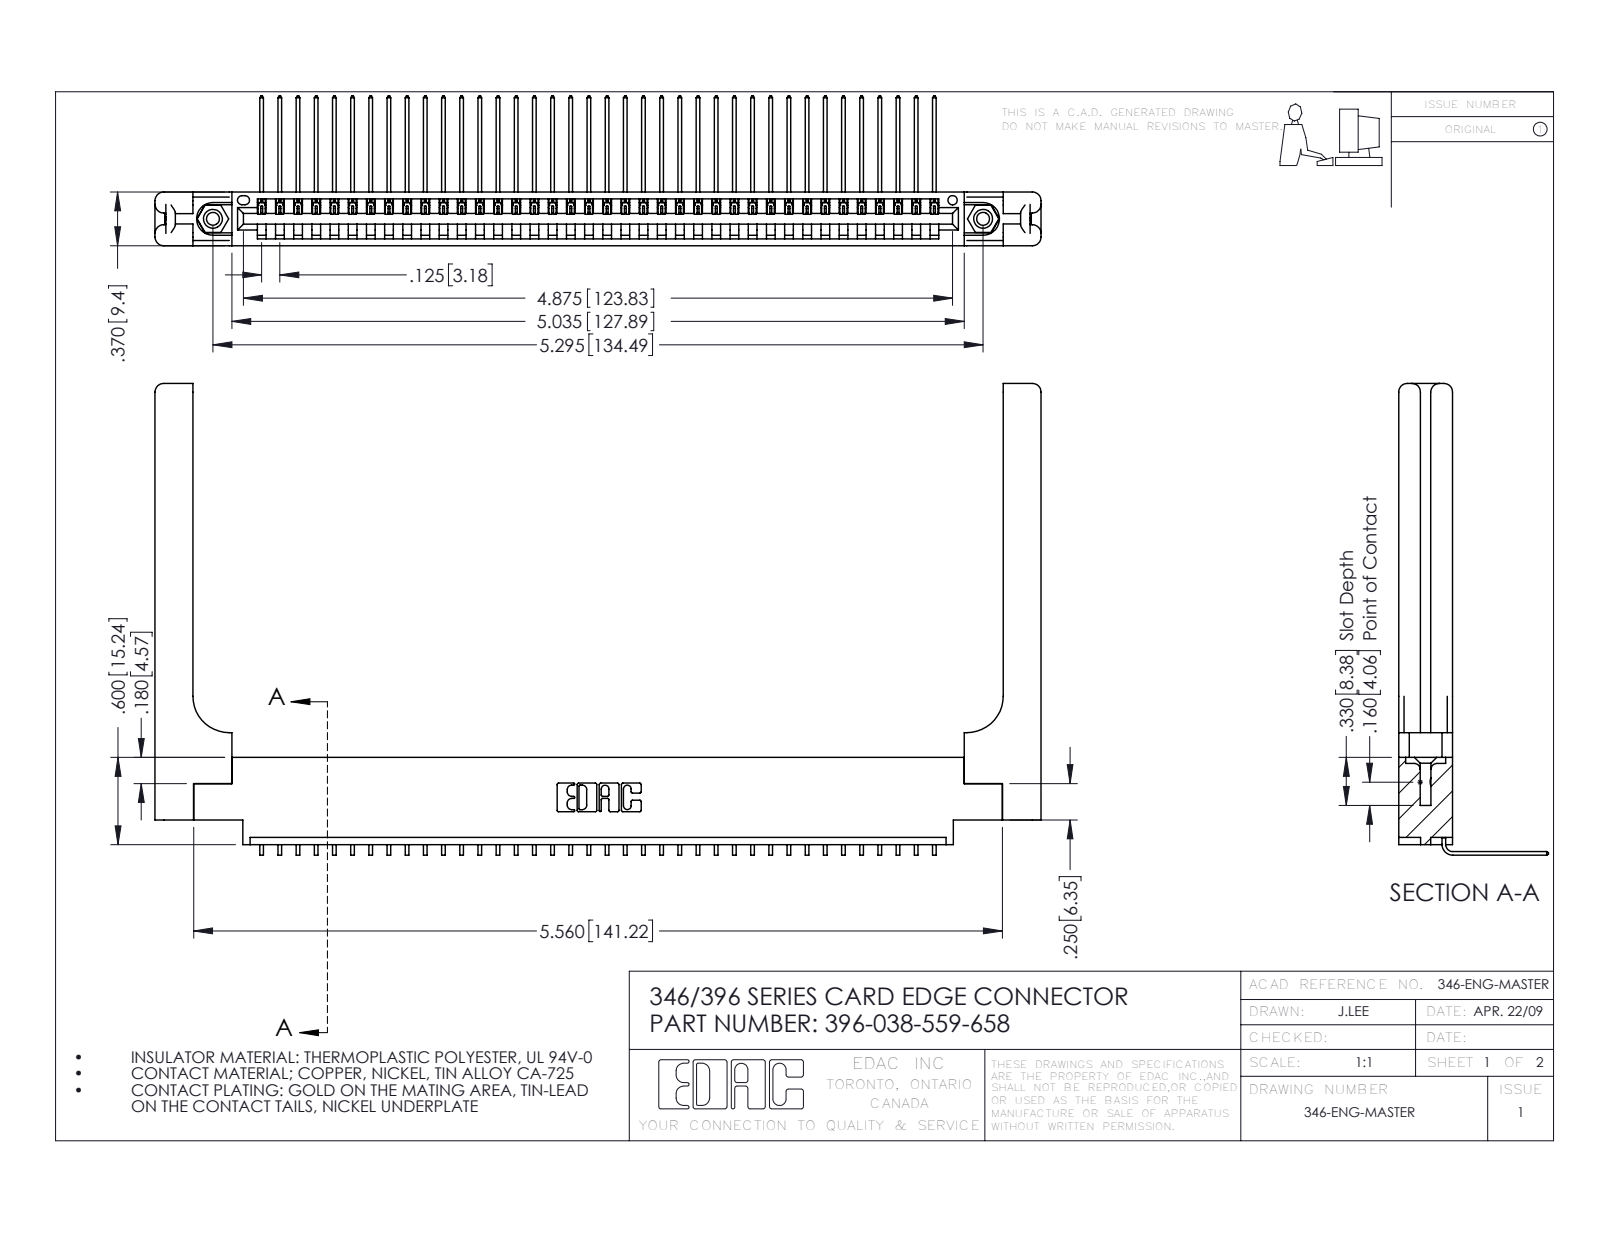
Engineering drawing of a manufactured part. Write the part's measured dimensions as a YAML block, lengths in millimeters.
part_name: "345-292-001_558 559 Tail - 1; 346 Part_0.170 Offset - 0.156 Dia-TH; 346-220-058_345-220-058; 345-250-001_345-250-001-102 (+1 more)"
step_written_by: "SolidWorks 2016 (CONFIG_CONTROL_DESIGN)"
units: millimeters
bodies: {solids: 43, faces: 2662, planar: 1824, cylindrical: 778, other: 60}
overall_size: [154.7, 82.4, 26.2]
volume: 22270
surface_area: 24480
round_holes:
  - {diameter: 2.3, count: 2}
  - {diameter: 3.2, count: 2}
  - {diameter: 4, count: 2}
  - {diameter: 1.6, count: 1}
round_bosses_or_shafts:
  - {diameter: 3.9, count: 2}
partial_cylinders:
  - {radius: 0.2, count: 76}
  - {radius: 0.3, count: 22}
  - {radius: 1.5, count: 16}
  - {radius: 0.2, count: 6}
  - {radius: 0.8, count: 6}
  - {radius: 0.7, count: 3}
  - {radius: 0.8, count: 2}
  - {radius: 0.8, count: 2}
face_to_face_distances: [9.4, 1.2, 1.8, 8.2, 3.8, 3.8, 0.6, 6.4, 7.6, 5.6]
hole_center_spacings: [6.2, 129.2, 134.5]
